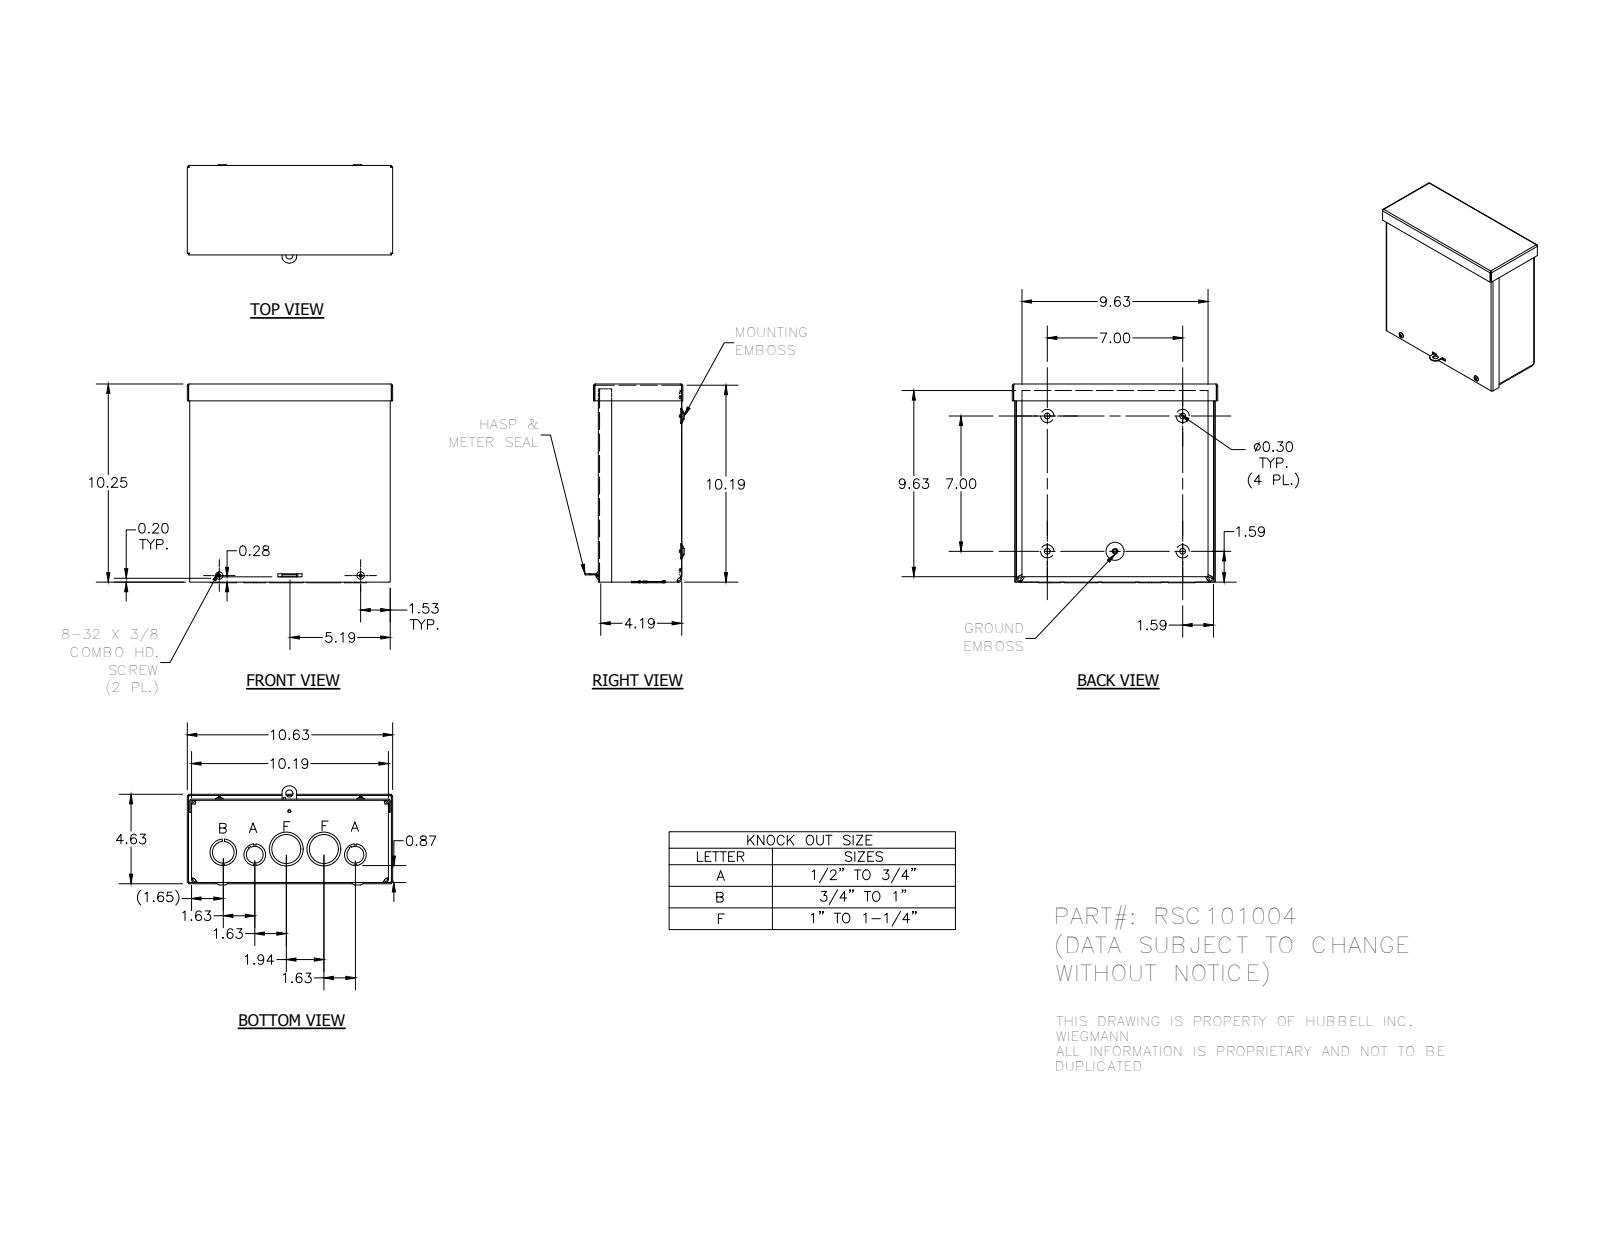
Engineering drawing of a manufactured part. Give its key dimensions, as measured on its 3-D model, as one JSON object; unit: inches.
{"part_name": "RSC101004; RSC101004_WRAP; RSC1010_LID; RSC1004_CAP (+4 more)", "step_written_by": "Autodesk Inventor 2012 (AUTOMOTIVE_DESIGN)", "units": "inches", "bodies": {"solids": 7, "faces": 518, "planar": 245, "cylindrical": 129, "other": 144}, "overall_size": [10.625, 10.281, 5.125], "volume_in3": 31.39, "surface_area_in2": 1029, "round_holes": [[0.3, 4], [0.313, 4], [1.125, 3], [0.125, 2], [0.148, 2], [0.875, 2], [1.5, 2], [1.75, 2], [0.156, 1], [0.165, 1], [0.375, 1], [1.375, 1]], "round_bosses_or_shafts": [[0.384, 2], [0.164, 2], [0.229, 1]], "partial_cylinders_radius": [[0.01, 10], [0.031, 8], [0.093, 8], [0.125, 8], [0.187, 8], [0.031, 4], [0.055, 4], [0.062, 4]], "face_to_face_distances": [0.062, 10.126, 0.062, 4.249, 4.187, 0.063, 4.312, 4.25, 10.188, 0.124], "hole_center_spacings": [7, 1.072, 1.261, 1.656, 3.5, 3.582, 7.313, 7.826]}
